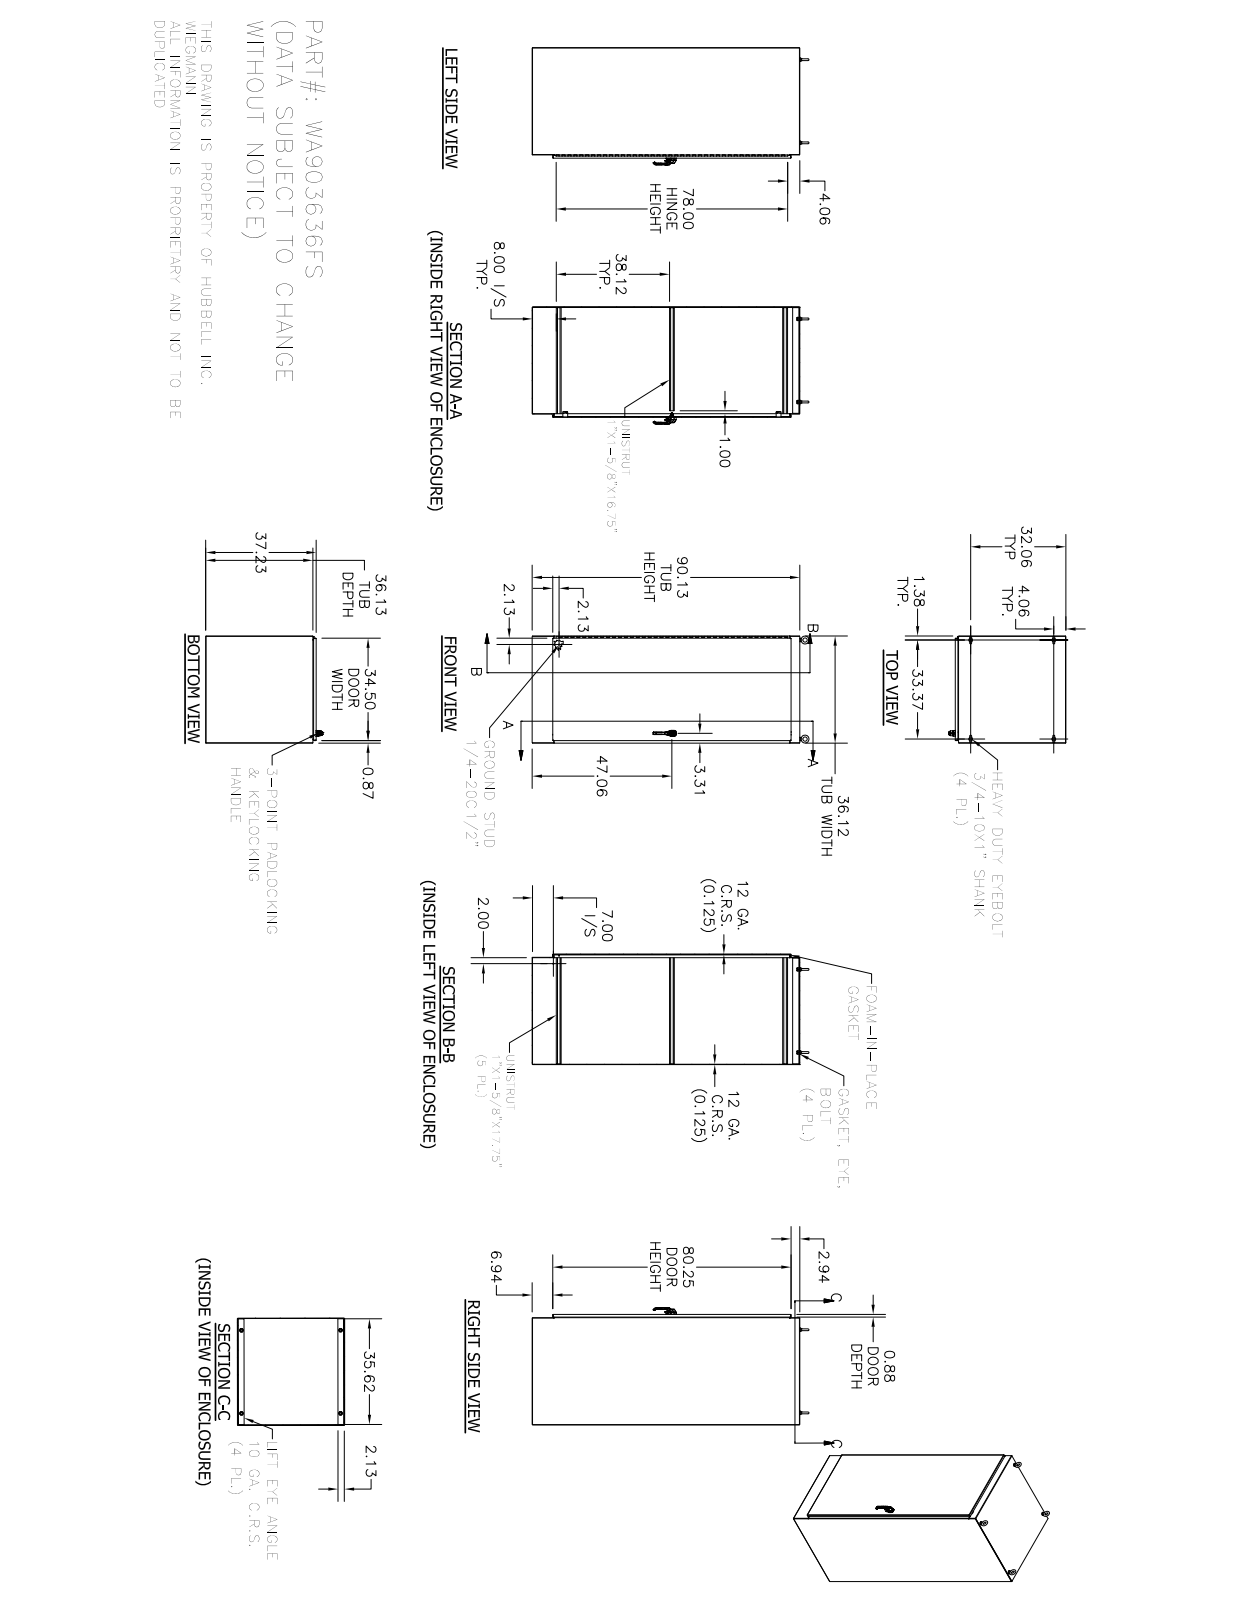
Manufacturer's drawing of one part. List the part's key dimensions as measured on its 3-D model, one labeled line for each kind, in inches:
Part name (STEP PRODUCT): WA9036FSFB; WA9036FSLS; WA9036FSRS; WA3636FSBTM-10GA (+8 more)
STEP written by: Autodesk Inventor 2014 (AUTOMOTIVE_DESIGN)
Units: inches
Bodies: 53 solids, 2982 faces (1231 planar, 1012 cylindrical, 739 other)
Overall size (bounding box): 93.248 × 39.478 × 36.125
Volume: 2 158 in³ · Surface area: 35 110 in²
Round holes (diameter × count): ⌀0.276 ×8, ⌀0.375 ×8, ⌀0.2 ×4, ⌀0.642 ×4, ⌀0.813 ×4, ⌀0.213 ×3, ⌀0.28 ×3, ⌀0.315 ×2, ⌀0.402 ×2, ⌀0.407 ×2, ⌀0.413 ×2, ⌀0.122 ×1
Round bosses / shafts (diameter × count): ⌀1.25 ×4, ⌀1.12 ×4, ⌀0.75 ×4, ⌀0.531 ×2, ⌀0.526 ×2, ⌀0.435 ×2, ⌀0.337 ×2, ⌀0.25 ×2
Partial cylindrical surfaces — rounded edges, fillets, slot ends (radius × count): R0.02 ×178, R0.012 ×100, R0.019 ×23, R0.01 ×16, R0.125 ×16, R0.031 ×14, R0.079 ×14, R0.156 ×14
Main face-to-face distances: 0.125, 36, 35.875, 36.125, 0.125, 36.98, 37.105, 37.23, 37.104, 90
Hole centre spacings: 8.667, 26, 17.333, 34.667, 0.38, 0.382, 0.382, 0.762
